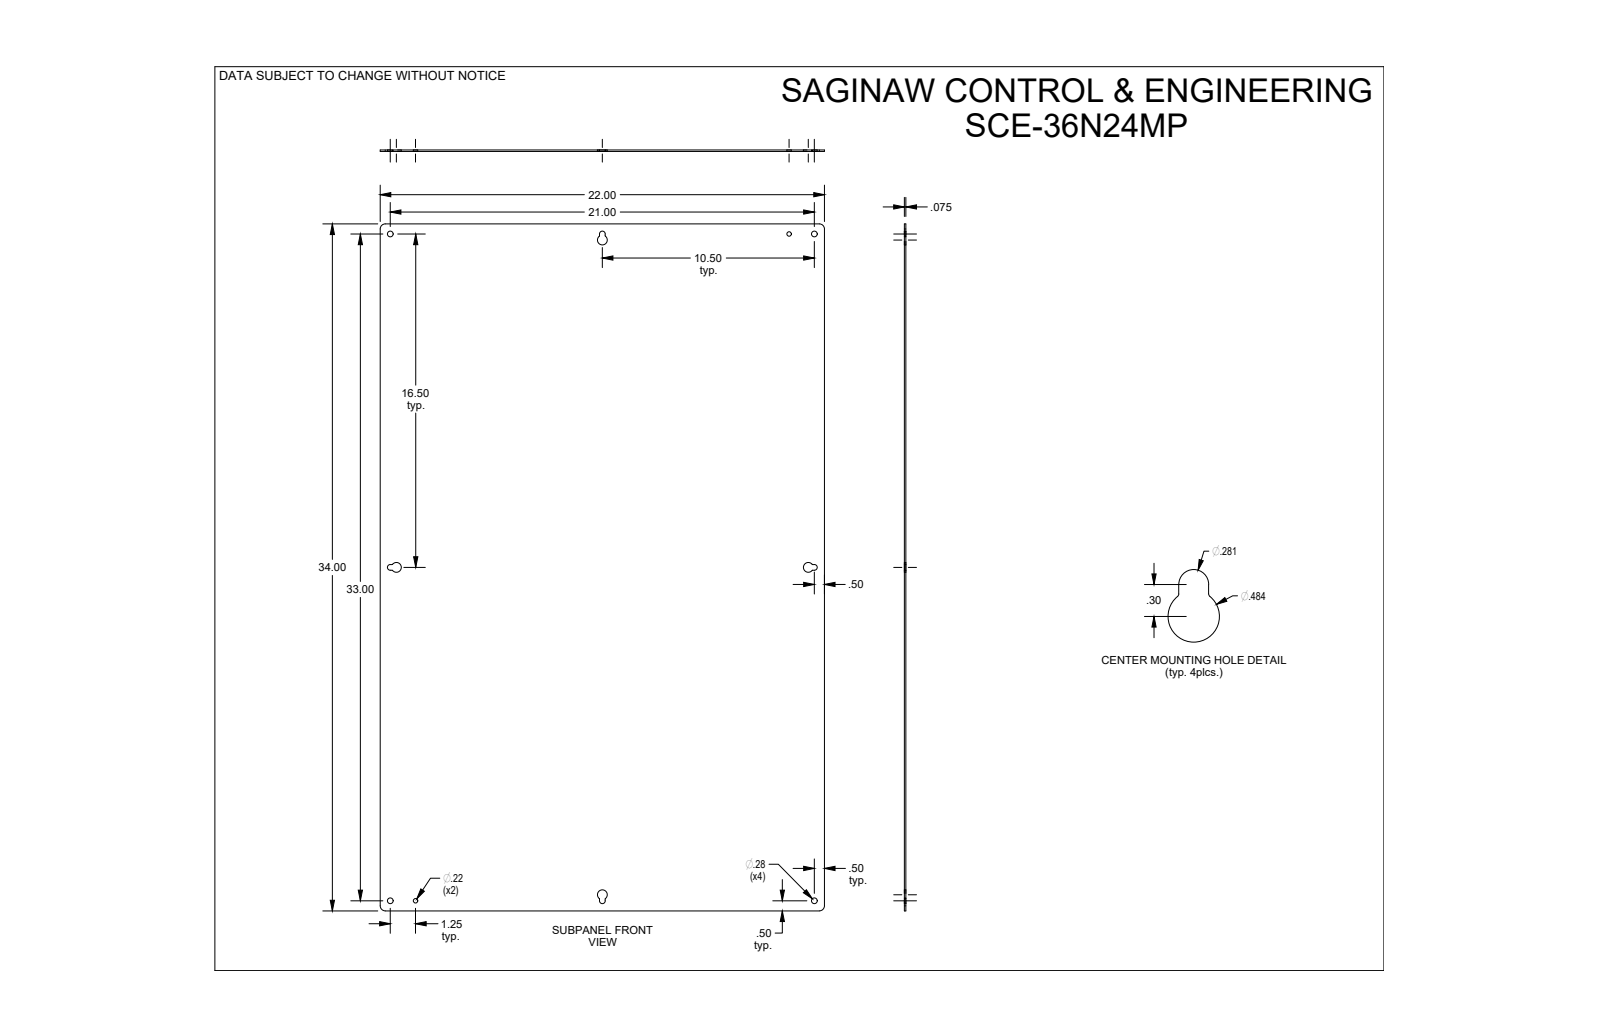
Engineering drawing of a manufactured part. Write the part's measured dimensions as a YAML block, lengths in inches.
part_name: "SCE-36N24MP"
step_written_by: "SolidWorks 2019 (CONFIG_CONTROL_DESIGN)"
units: inches
bodies: {solids: 1, faces: 40, planar: 14, cylindrical: 26, other: 0}
overall_size: [34, 22, 0.075]
volume: 56
surface_area: 1503
round_holes:
  - {diameter: 0.281, count: 4}
  - {diameter: 0.218, count: 2}
partial_cylinders:
  - {radius: 0.03, count: 8}
  - {radius: 0.141, count: 4}
  - {radius: 0.242, count: 4}
  - {radius: 0.25, count: 4}
face_to_face_distances: [0.075, 22, 34, 16.859, 17.141, 0.281, 10.859, 11.141]
hole_center_spacings: [1.25, 19.75, 21, 33, 33.024, 38.459, 39.115, 37.832]
